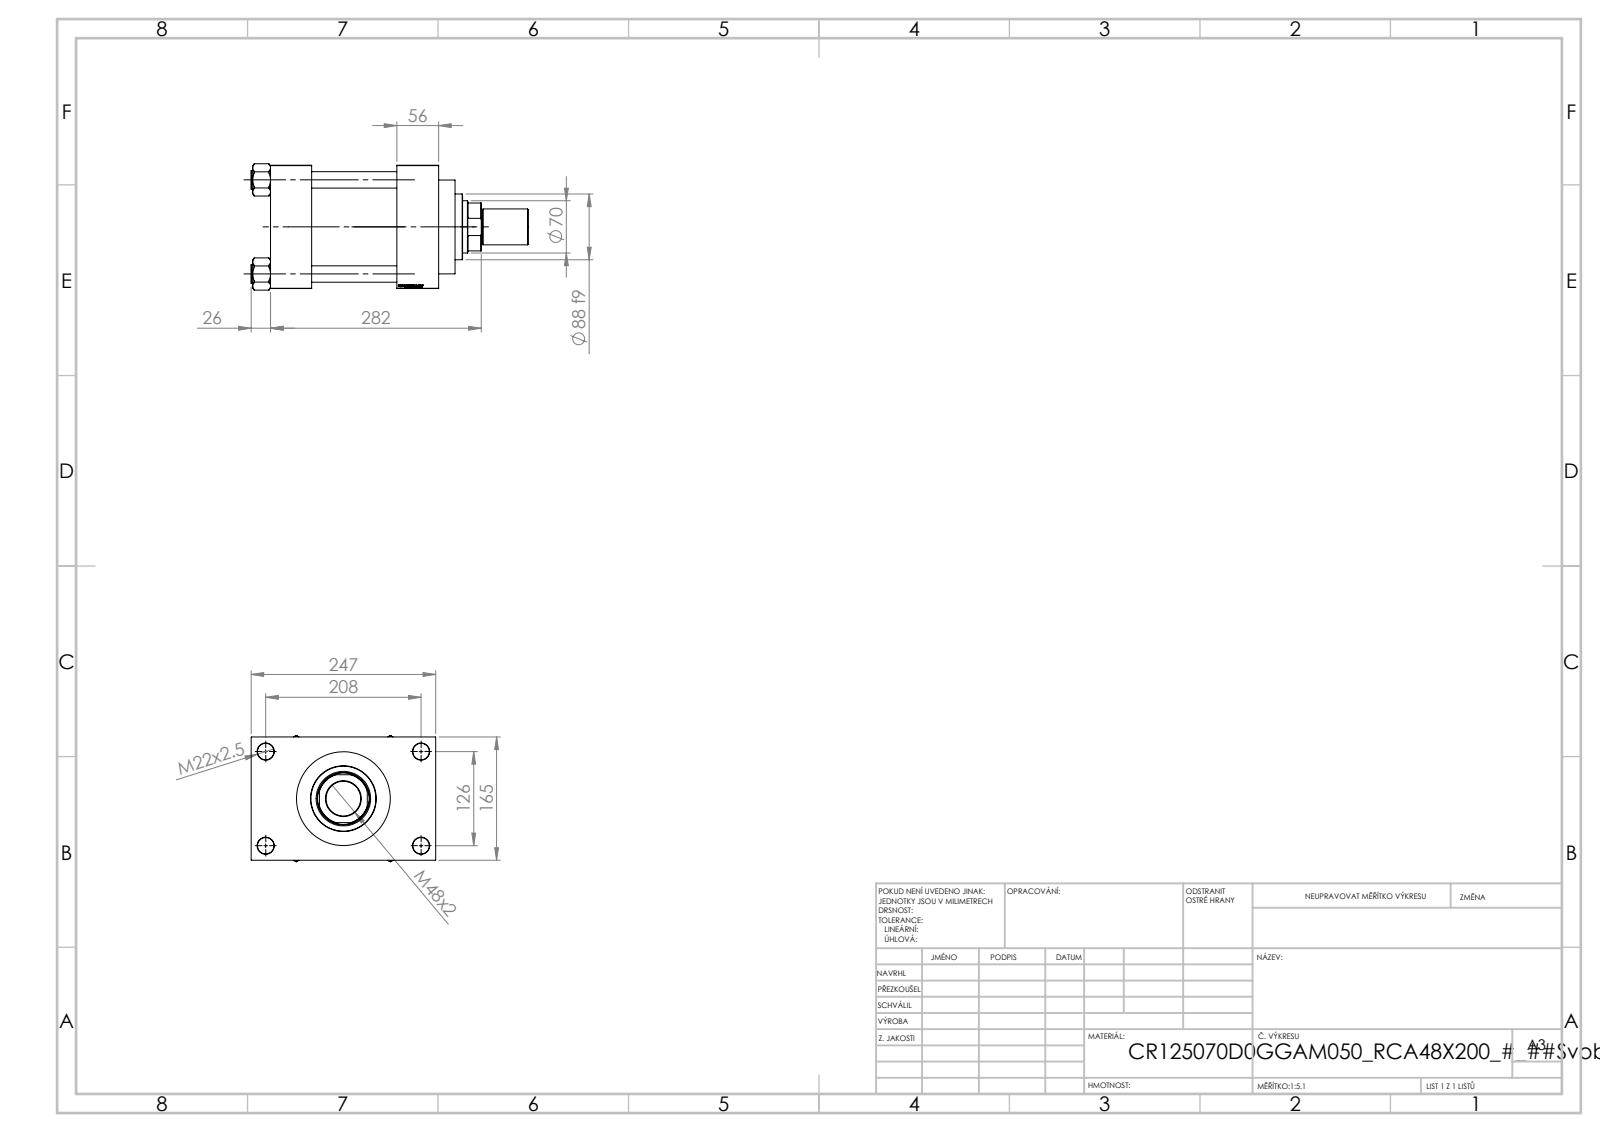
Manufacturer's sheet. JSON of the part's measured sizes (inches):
{"part_name": "V215_VC_A; V215CR_D_TYCINKA; ROD_END_AH; V215CR_D_Body (+2 more)", "step_written_by": "SolidWorks 2019 (CONFIG_CONTROL_DESIGN)", "units": "inches", "bodies": {"solids": 12, "faces": 1163, "planar": 548, "cylindrical": 91, "other": 524}, "overall_size": [14.606, 9.724, 6.659], "volume_in3": 326.9, "surface_area_in2": 914.9, "round_holes": [[0.866, 8], [0.276, 2], [1.269, 2], [1.772, 2], [1.831, 1], [2.756, 1], [2.874, 1], [3.78, 1], [4.921, 1], [4.941, 1]], "round_bosses_or_shafts": [[0.984, 4], [5.157, 1], [3.465, 1], [1.89, 1], [1.811, 1]], "partial_cylinders_radius": [[1.339, 1]], "face_to_face_distances": [4.488, 6.496, 2.165, 6.654, 8.858, 6.693, 2.205, 1.614, 8.11, 9.724], "hole_center_spacings": [1.616, 3.505, 4.787, 4.957, 5.215, 6.573, 8.233, 4.961]}
